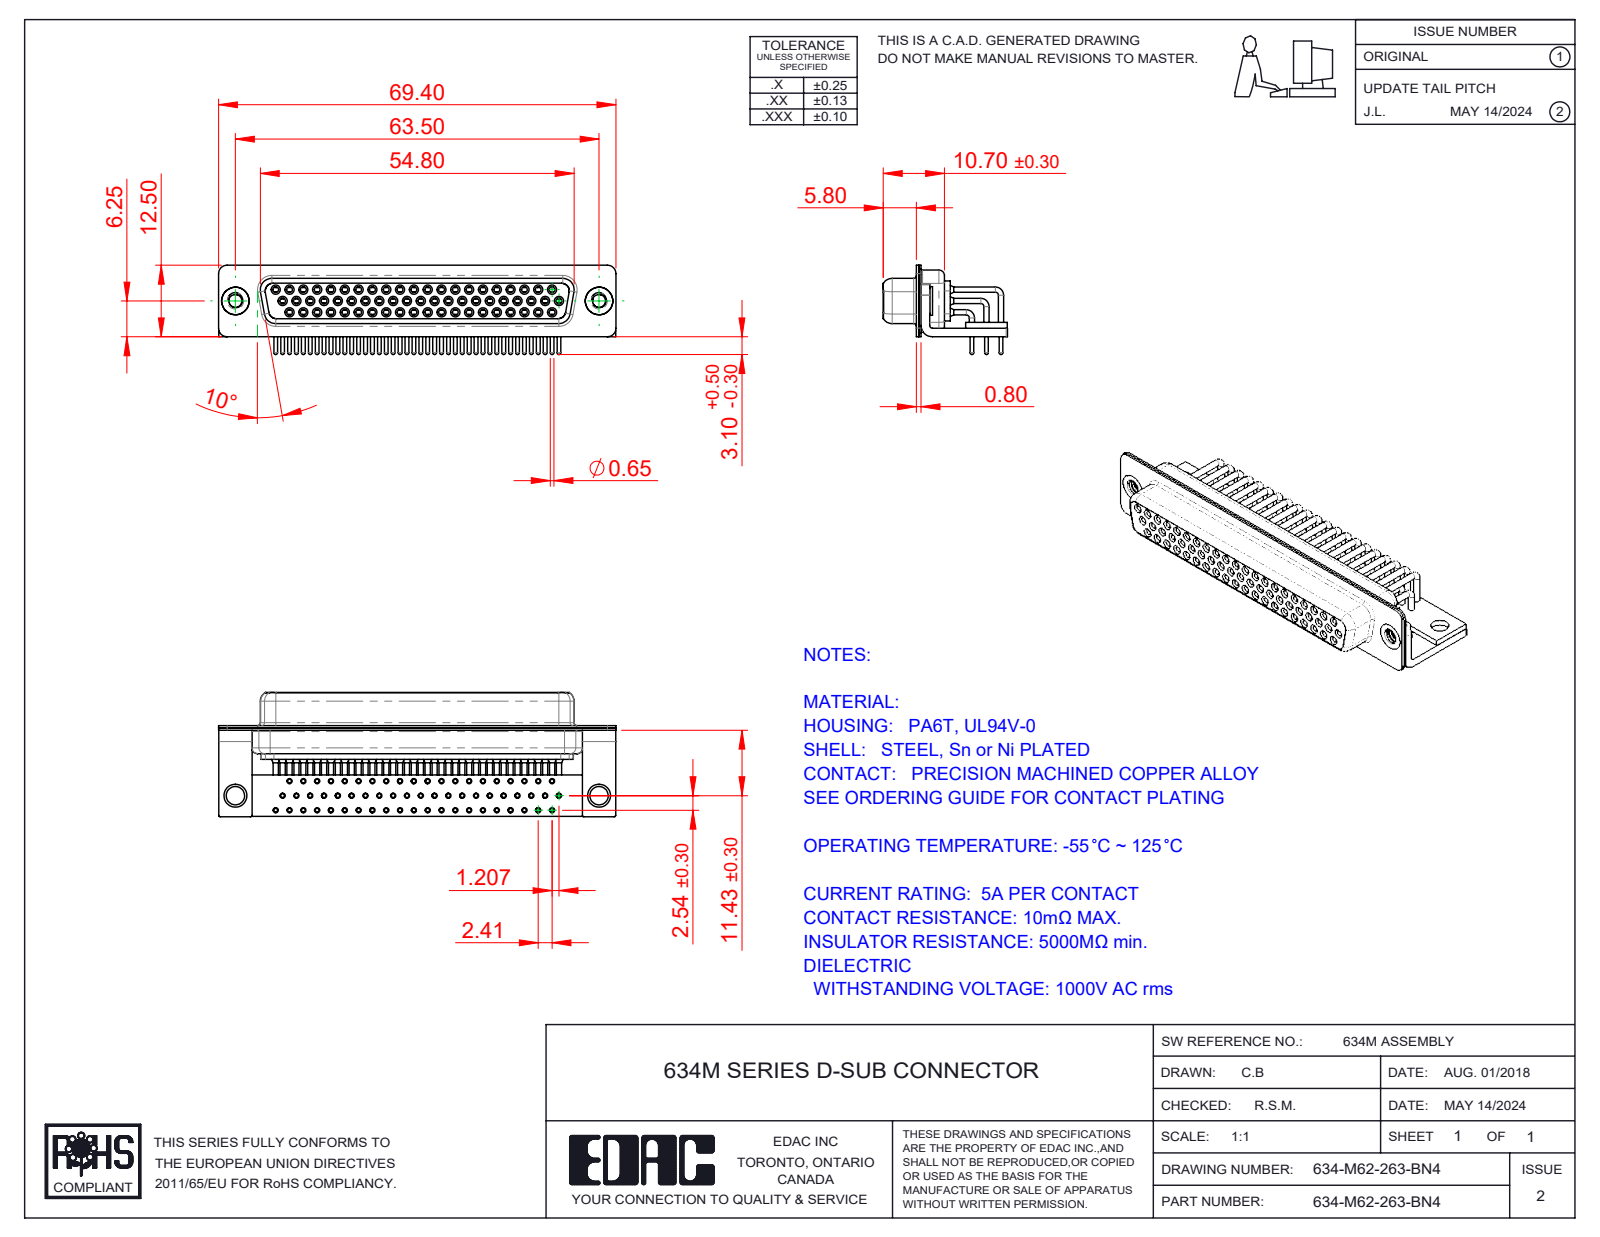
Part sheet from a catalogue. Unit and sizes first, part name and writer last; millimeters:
Units: millimetres
Overall size (bounding box): 69.4 × 21.7 × 15.6
Round holes (diameter × count): ⌀0.9 ×62, ⌀1 ×62, ⌀1.1 ×62, ⌀1.7 ×62, ⌀1.8 ×62, ⌀2 ×62, ⌀2.26 ×2, ⌀3.2 ×2, ⌀4 ×2, ⌀4.8 ×2
Round bosses / shafts (diameter × count): ⌀0.9 ×118, ⌀1.6 ×62, ⌀1.5 ×62, ⌀0.65 ×62, ⌀2 ×56, ⌀5 ×2, ⌀4.9 ×2
Partial cylindrical surfaces — rounded edges, fillets, slot ends (radius × count): R0.25 ×16, R1.5 ×16, R2 ×13, R1.35 ×8, R1.6 ×8, R0.5 ×5, R0.6 ×4, R0.65 ×4
Main face-to-face distances: 0.4, 2.3, 1.9, 1, 1.45, 8.95, 8.5, 0.85, 0.8, 9.35
Hole centre spacings: 7.24, 2.41, 9.65, 4.83, 14.48, 16.89, 2.81, 2.32
Volume: 6 132 mm³ · Surface area: 19 720 mm²
Bodies: 70 solids, 3739 faces (1023 planar, 1709 cylindrical, 1007 other)
Part name (STEP PRODUCT): 634M 4-40 Threaded Rivet_Stabilizer; 634M Contact Row 1; 634M Shell Front_62 Contacts; 634M Contact Row 2 (+6 more)
STEP written by: SolidWorks 2016 (CONFIG_CONTROL_DESIGN)
